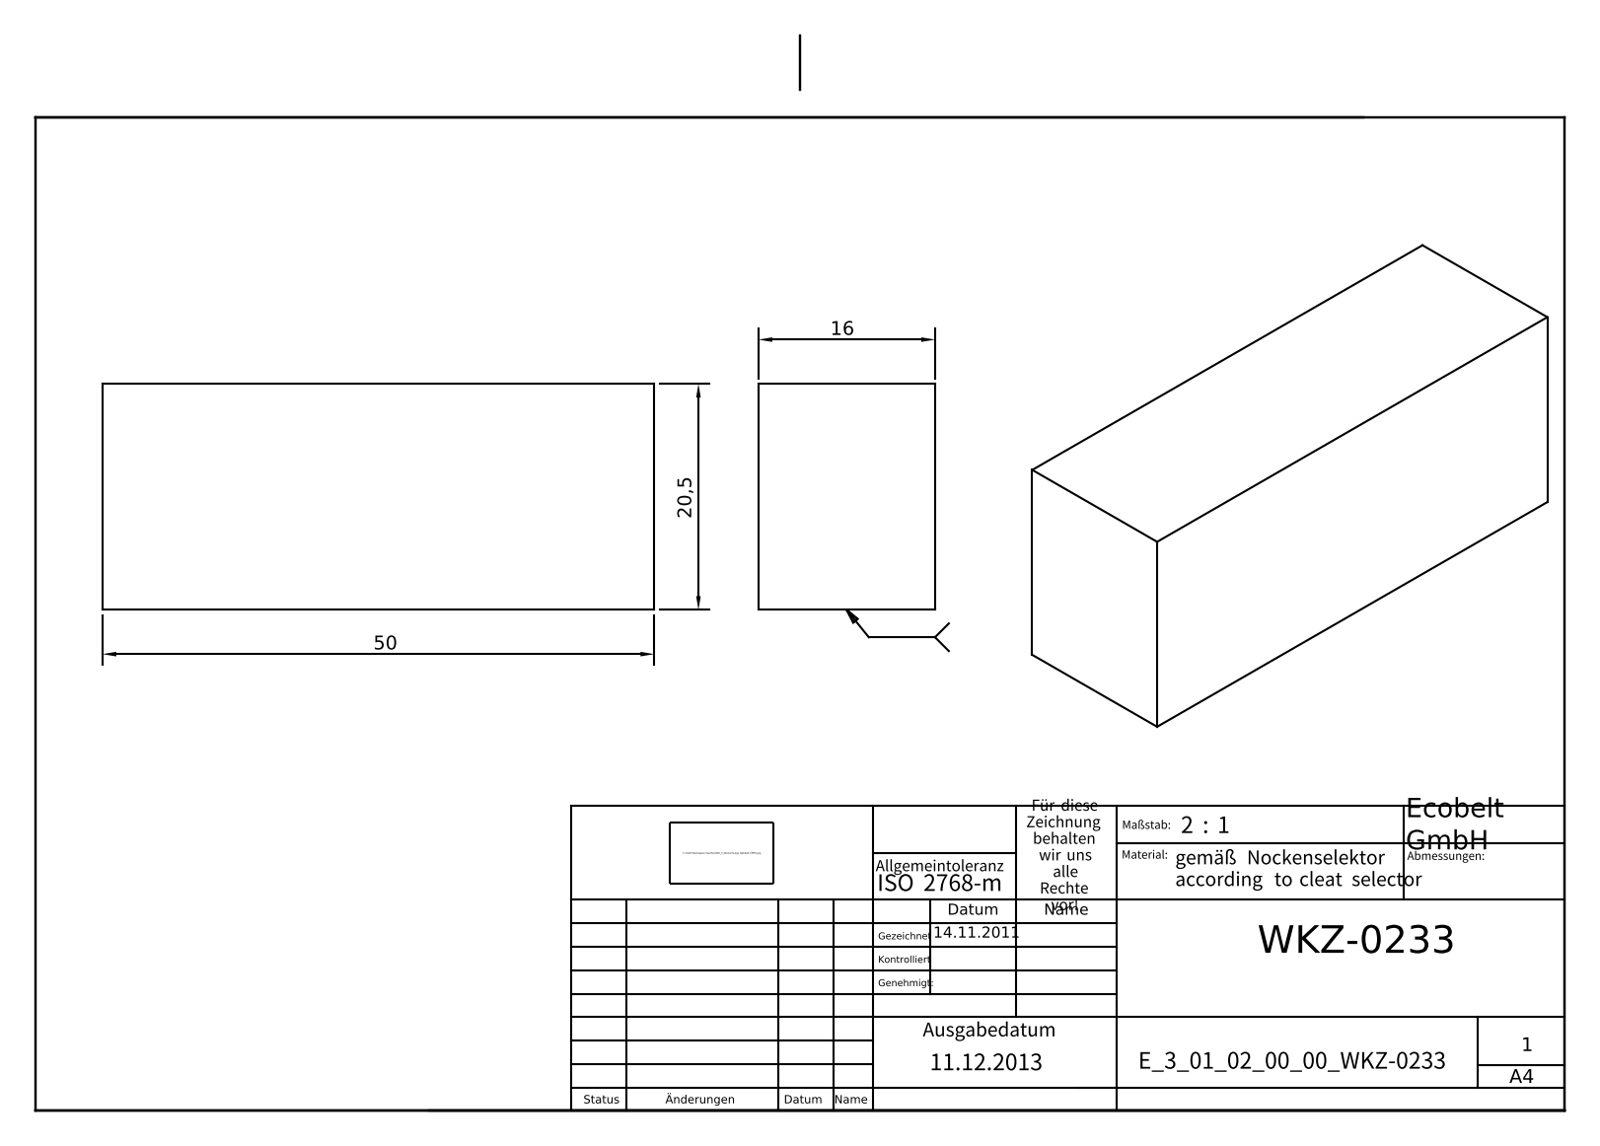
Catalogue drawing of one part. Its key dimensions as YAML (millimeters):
part_name: "E_3_01_02_00_00_WKZ-0233"
step_written_by: "Autodesk Inventor 2021 (AUTOMOTIVE_DESIGN)"
units: millimeters
bodies: {solids: 1, faces: 6, planar: 6, cylindrical: 0, other: 0}
overall_size: [50, 20.5, 16]
volume: 16400
surface_area: 4306
face_to_face_distances: [16, 20.5, 50]
